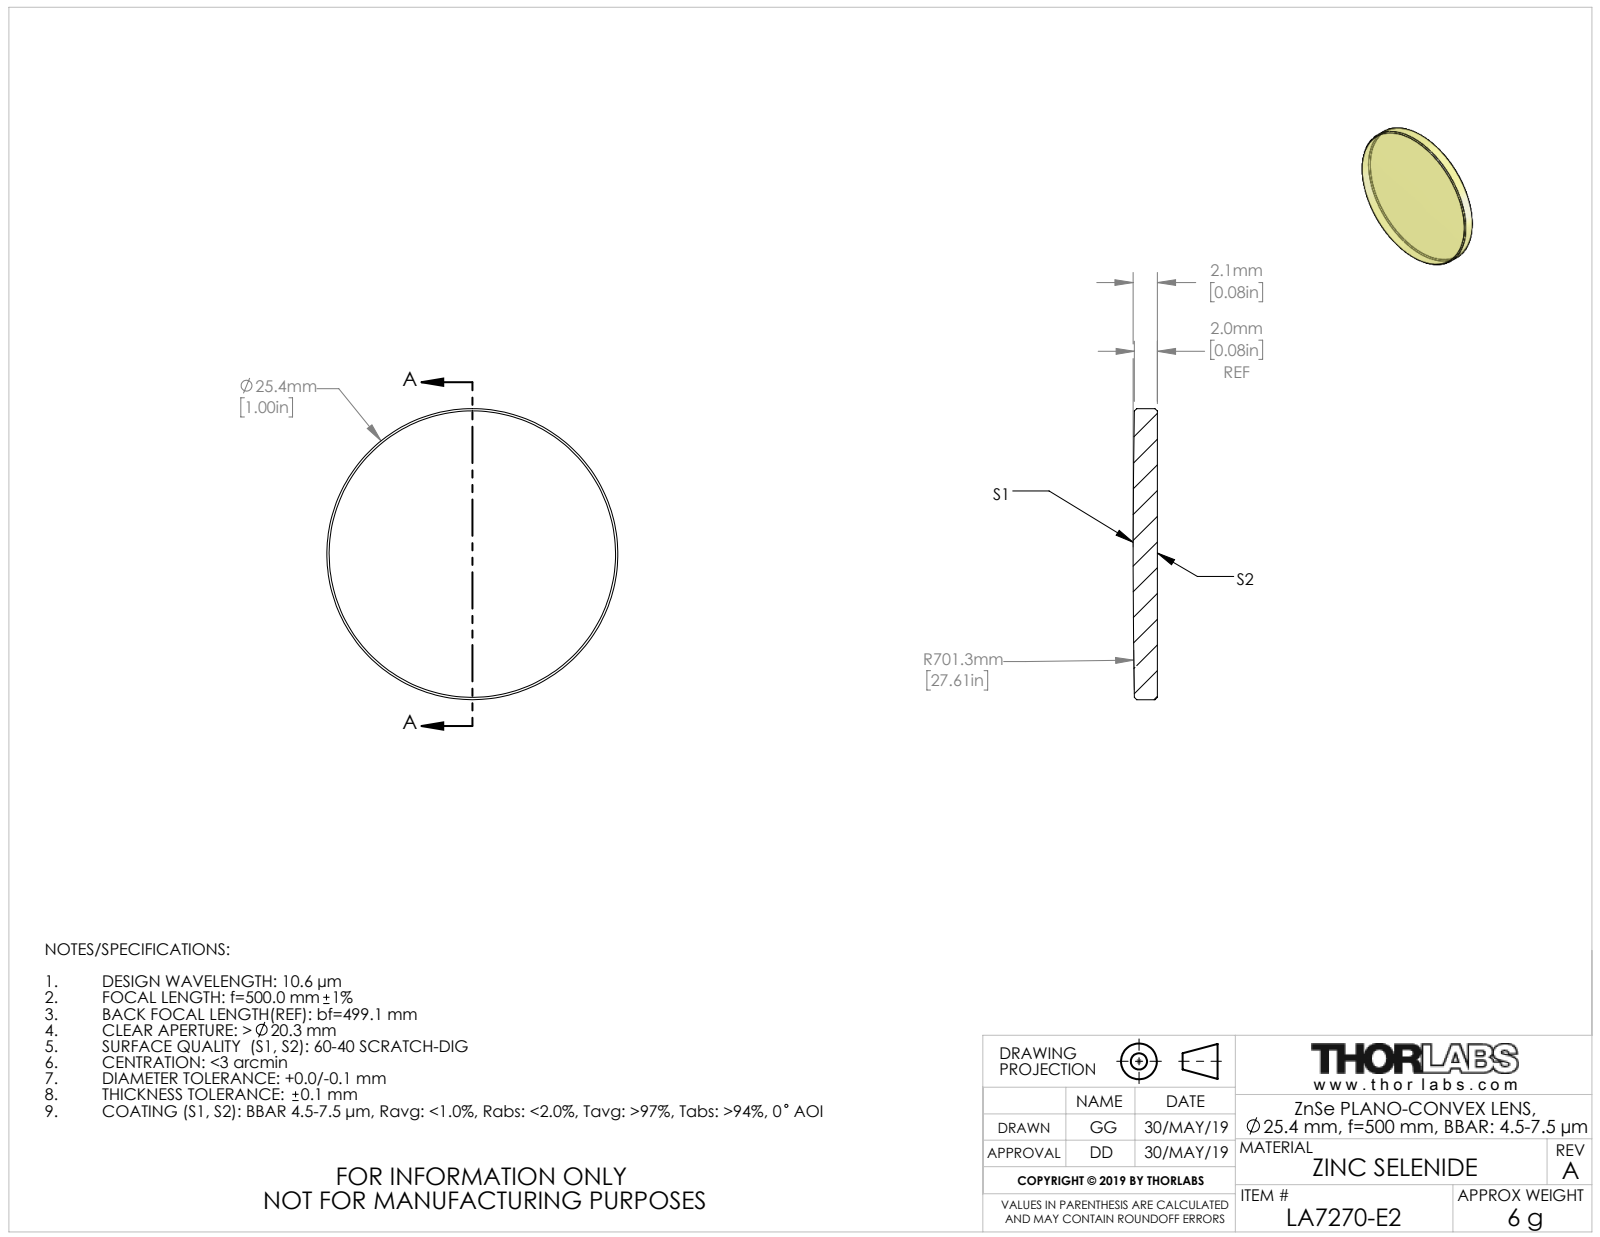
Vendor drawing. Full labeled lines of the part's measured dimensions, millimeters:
Part name (STEP PRODUCT): TTN047612-E0W
STEP written by: SolidWorks 2018 (CONFIG_CONTROL_DESIGN)
Units: millimetres
Bodies: 1 solid, 9 faces (1 planar, 2 cylindrical, 6 other)
Overall size (bounding box): 25.4 × 25.4 × 2.11
Volume: 1 037 mm³ · Surface area: 1 154 mm²
Round bosses / shafts (diameter × count): ⌀25.4 ×1
